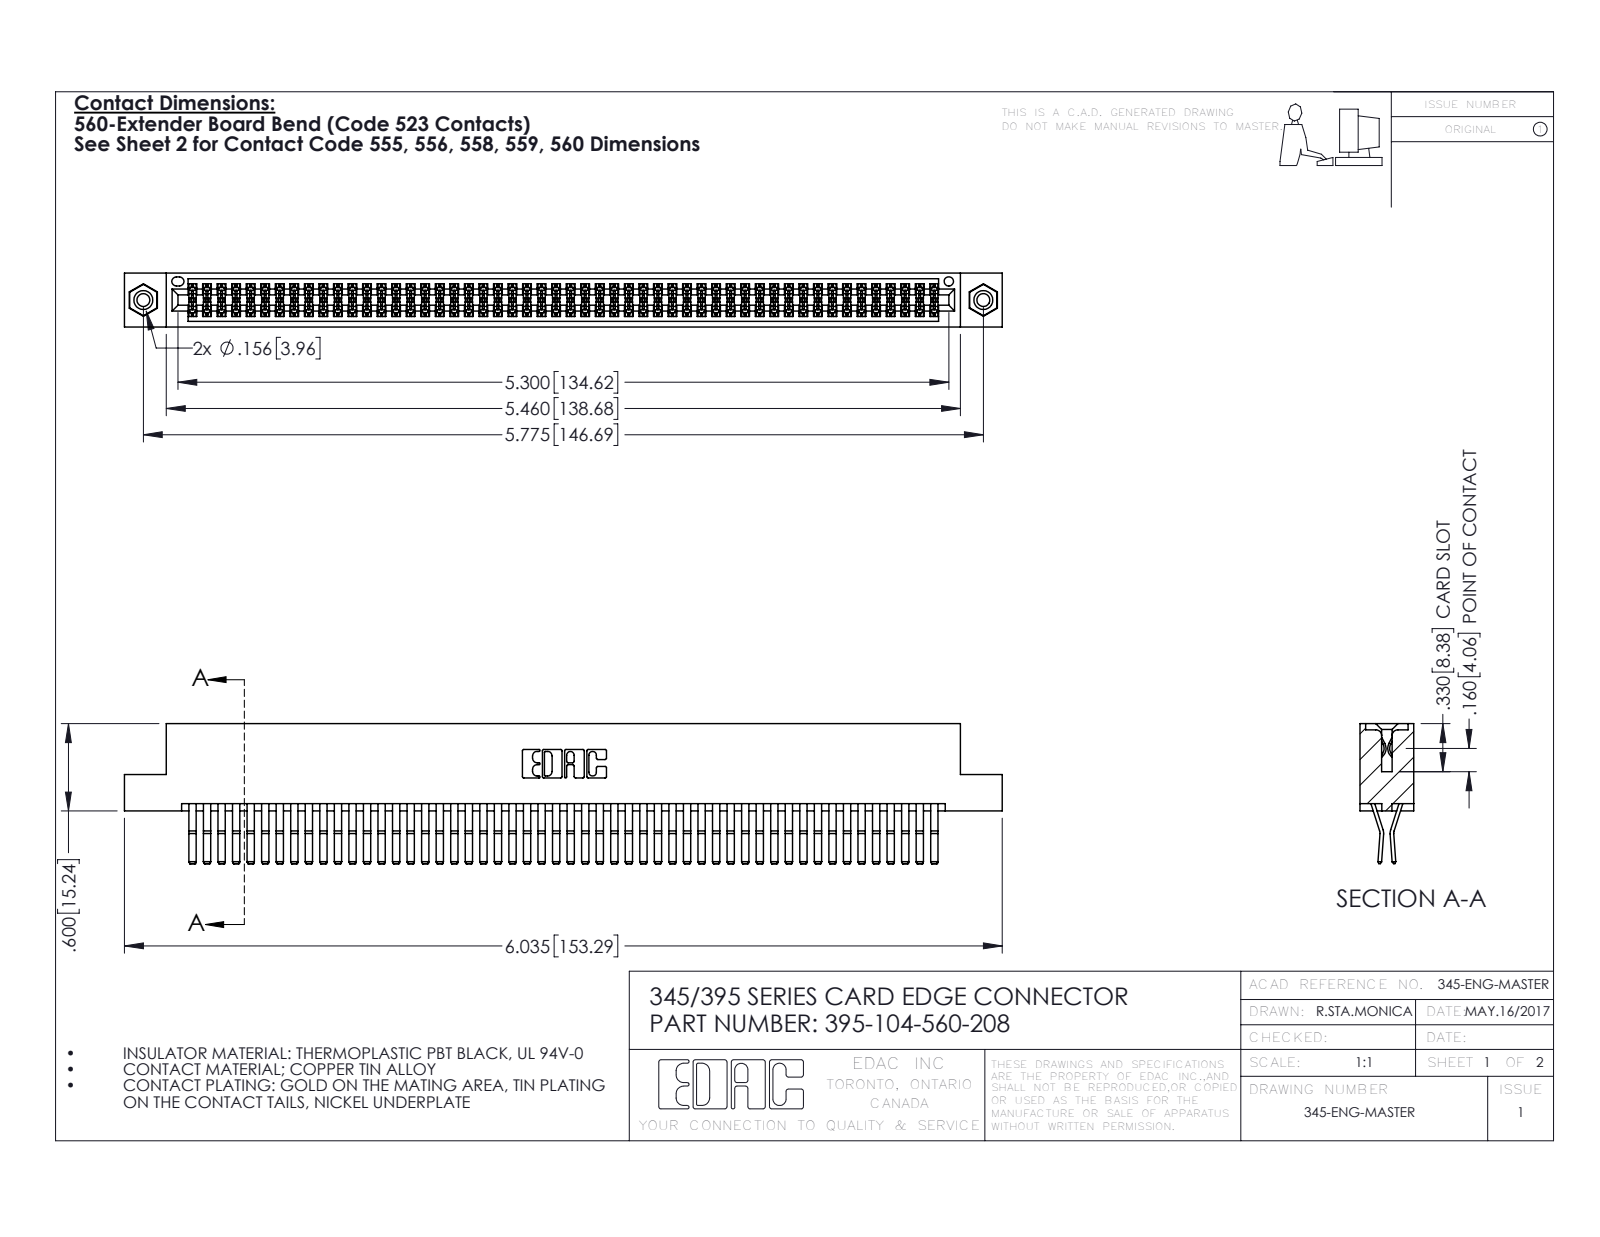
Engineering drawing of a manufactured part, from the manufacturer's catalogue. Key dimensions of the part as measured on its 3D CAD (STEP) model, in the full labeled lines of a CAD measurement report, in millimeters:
Part name (STEP PRODUCT): 345-292-001_560 Tail; 345 Part_Flush Mounting Lugs - 0.156 Dia-TI; 345-250-001_345-250-003-102; 395-104-560-208
STEP written by: SolidWorks 2016 (CONFIG_CONTROL_DESIGN)
Units: millimetres
Bodies: 107 solids, 5594 faces (3544 planar, 2034 cylindrical, 16 other)
Overall size (bounding box): 153.3 × 24.4 × 9.4
Volume: 15 700 mm³ · Surface area: 25 110 mm²
Round holes (diameter × count): ⌀2.3 ×2, ⌀3.2 ×2, ⌀4 ×2, ⌀1.6 ×1
Round bosses / shafts (diameter × count): ⌀3.9 ×2
Partial cylindrical surfaces — rounded edges, fillets, slot ends (radius × count): R0.2 ×157, R0.3 ×22, R0.2 ×6, R0.8 ×6, R0.7 ×3, R0.3 ×2, R0.4 ×2, R0.5 ×2
Main face-to-face distances: 0.6, 1.8, 7.6, 9.4, 5.1, 2.5, 6.9, 5.7, 4.4, 3.8
Hole centre spacings: 6.9, 140.7, 146.7
